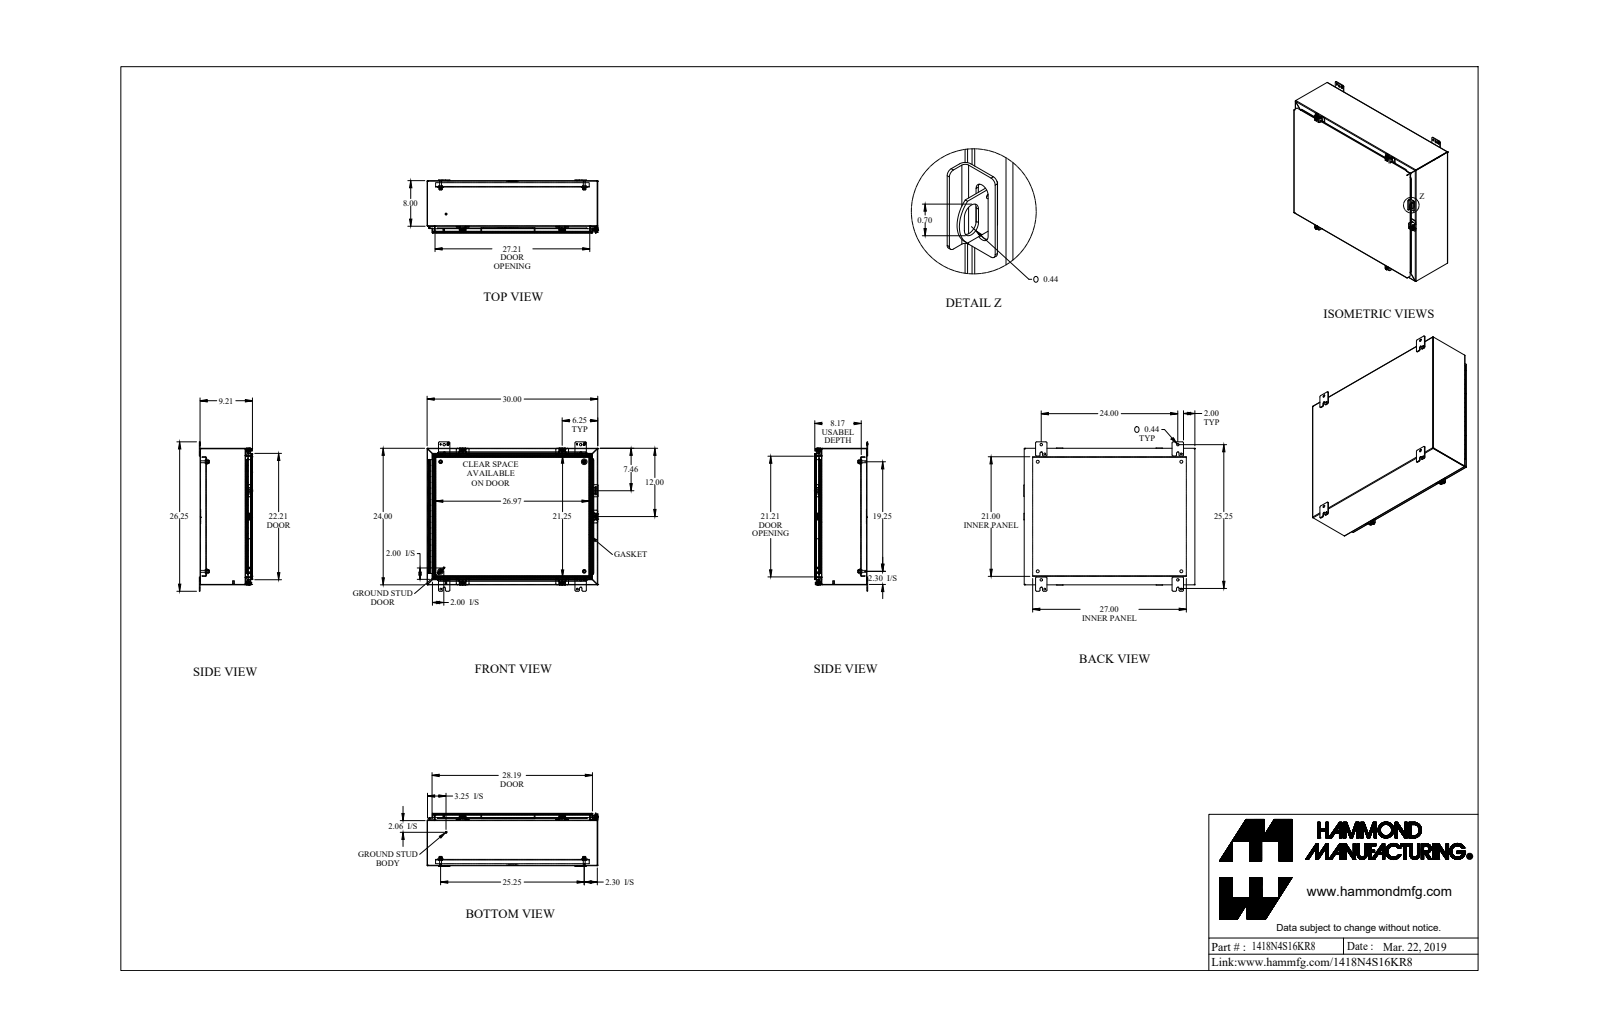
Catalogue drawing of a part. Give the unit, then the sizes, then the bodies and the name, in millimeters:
Units: millimetres
Overall size (bounding box): 763.6 × 666.8 × 238.1
Round holes (diameter × count): ⌀5.4 ×5, ⌀6.7 ×5, ⌀9.5 ×5, ⌀8 ×4, ⌀11.1 ×4, ⌀12.7 ×4, ⌀7.8 ×2, ⌀11.3 ×2, ⌀2.8 ×1, ⌀3.2 ×1
Round bosses / shafts (diameter × count): ⌀12.7 ×5, ⌀9.9 ×5, ⌀6.2 ×5, ⌀16.5 ×4, ⌀9.5 ×4, ⌀8.4 ×4, ⌀25.4 ×2, ⌀8 ×2
Partial cylindrical surfaces — rounded edges, fillets, slot ends (radius × count): R4.8 ×26, R0.9 ×24, R2.7 ×24, R6.4 ×24, R1.2 ×21, R3.6 ×21, R3.2 ×12, R3.6 ×10
Main face-to-face distances: 1.8, 1.8, 230.3, 232.1, 232.1, 233.9, 2.4, 23.8, 25.6, 205.9
Hole centre spacings: 527.3, 609.6, 857.6, 112.3, 489, 545.6, 551.8, 767.8
Volume: 4 208 000 mm³ · Surface area: 4 342 000 mm²
Bodies: 43 solids, 1485 faces (806 planar, 539 cylindrical, 140 other)
Part name (STEP PRODUCT): 1418N4S16KR8_Default
STEP written by: SolidWorks 2019 (CONFIG_CONTROL_DESIGN)
